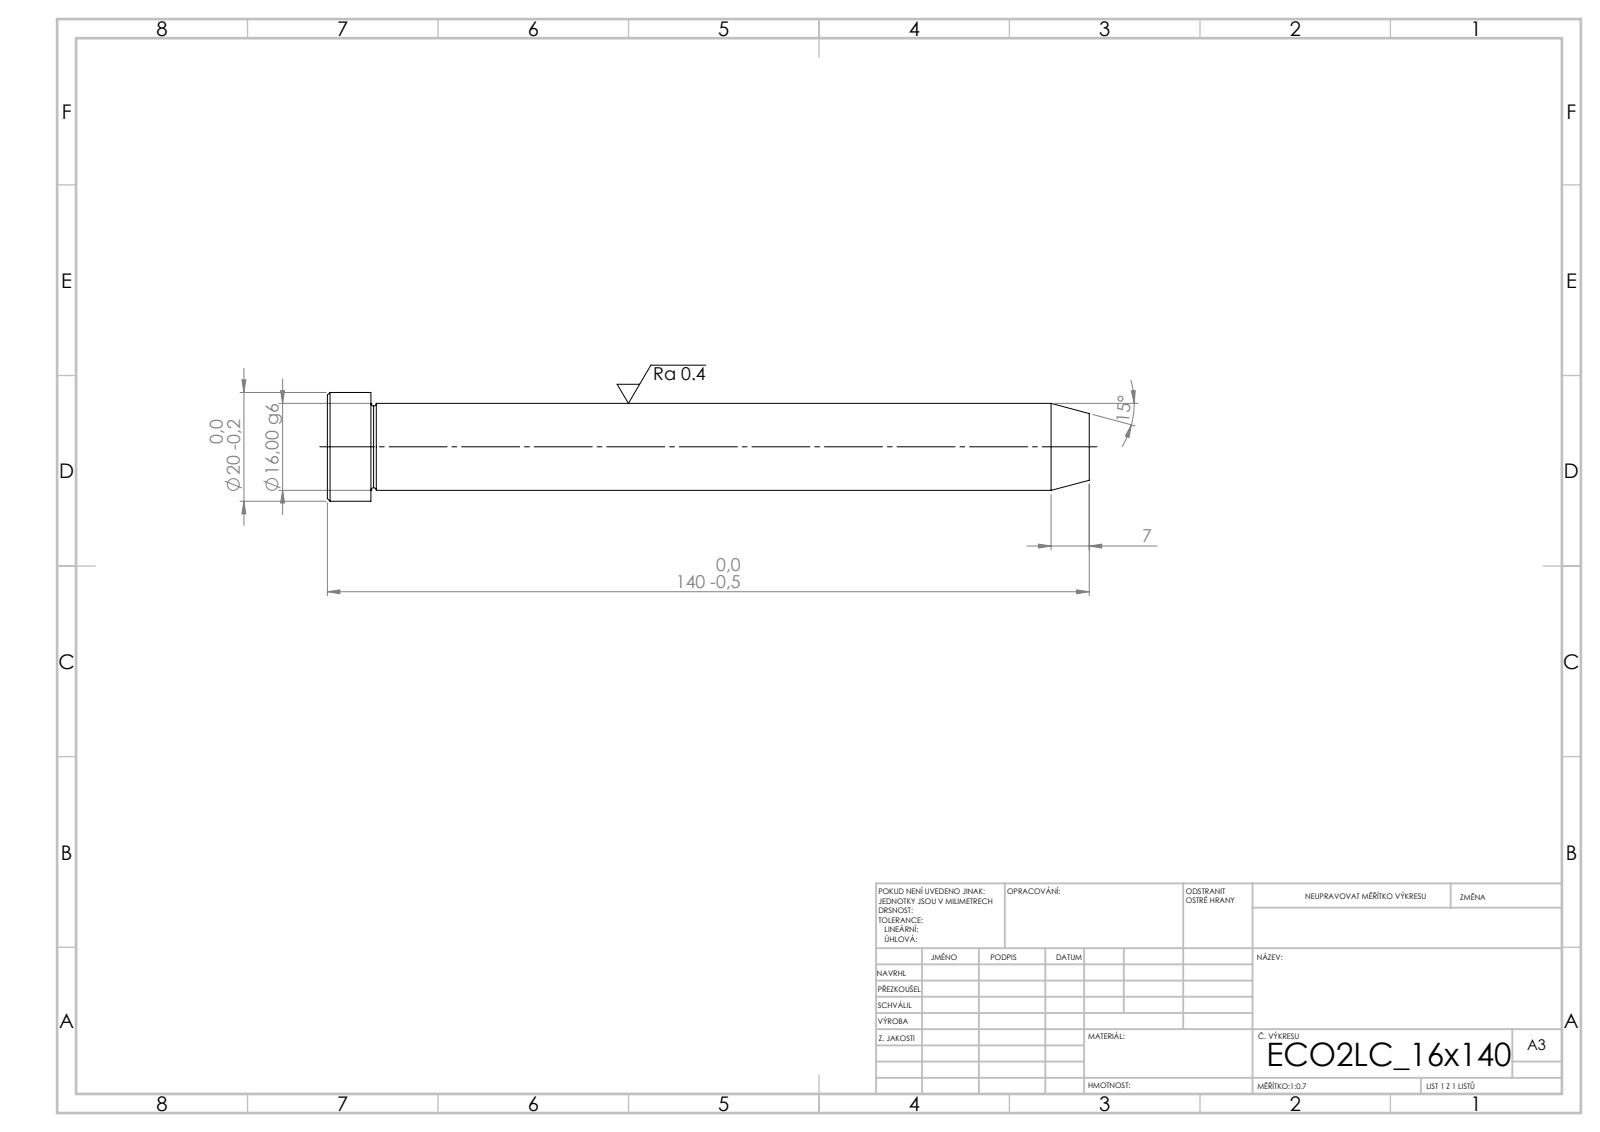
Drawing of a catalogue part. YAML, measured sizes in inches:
step_written_by: "SolidWorks 2019 (CONFIG_CONTROL_DESIGN)"
units: inches
bodies: {solids: 1, faces: 15, planar: 3, cylindrical: 4, other: 8}
overall_size: [5.512, 0.787, 0.787]
volume: 1.753
surface_area: 11.87
round_bosses_or_shafts:
  - {diameter: 0.787, count: 1}
  - {diameter: 0.63, count: 1}
face_to_face_distances: [5.512, 5.197, 0.315]
